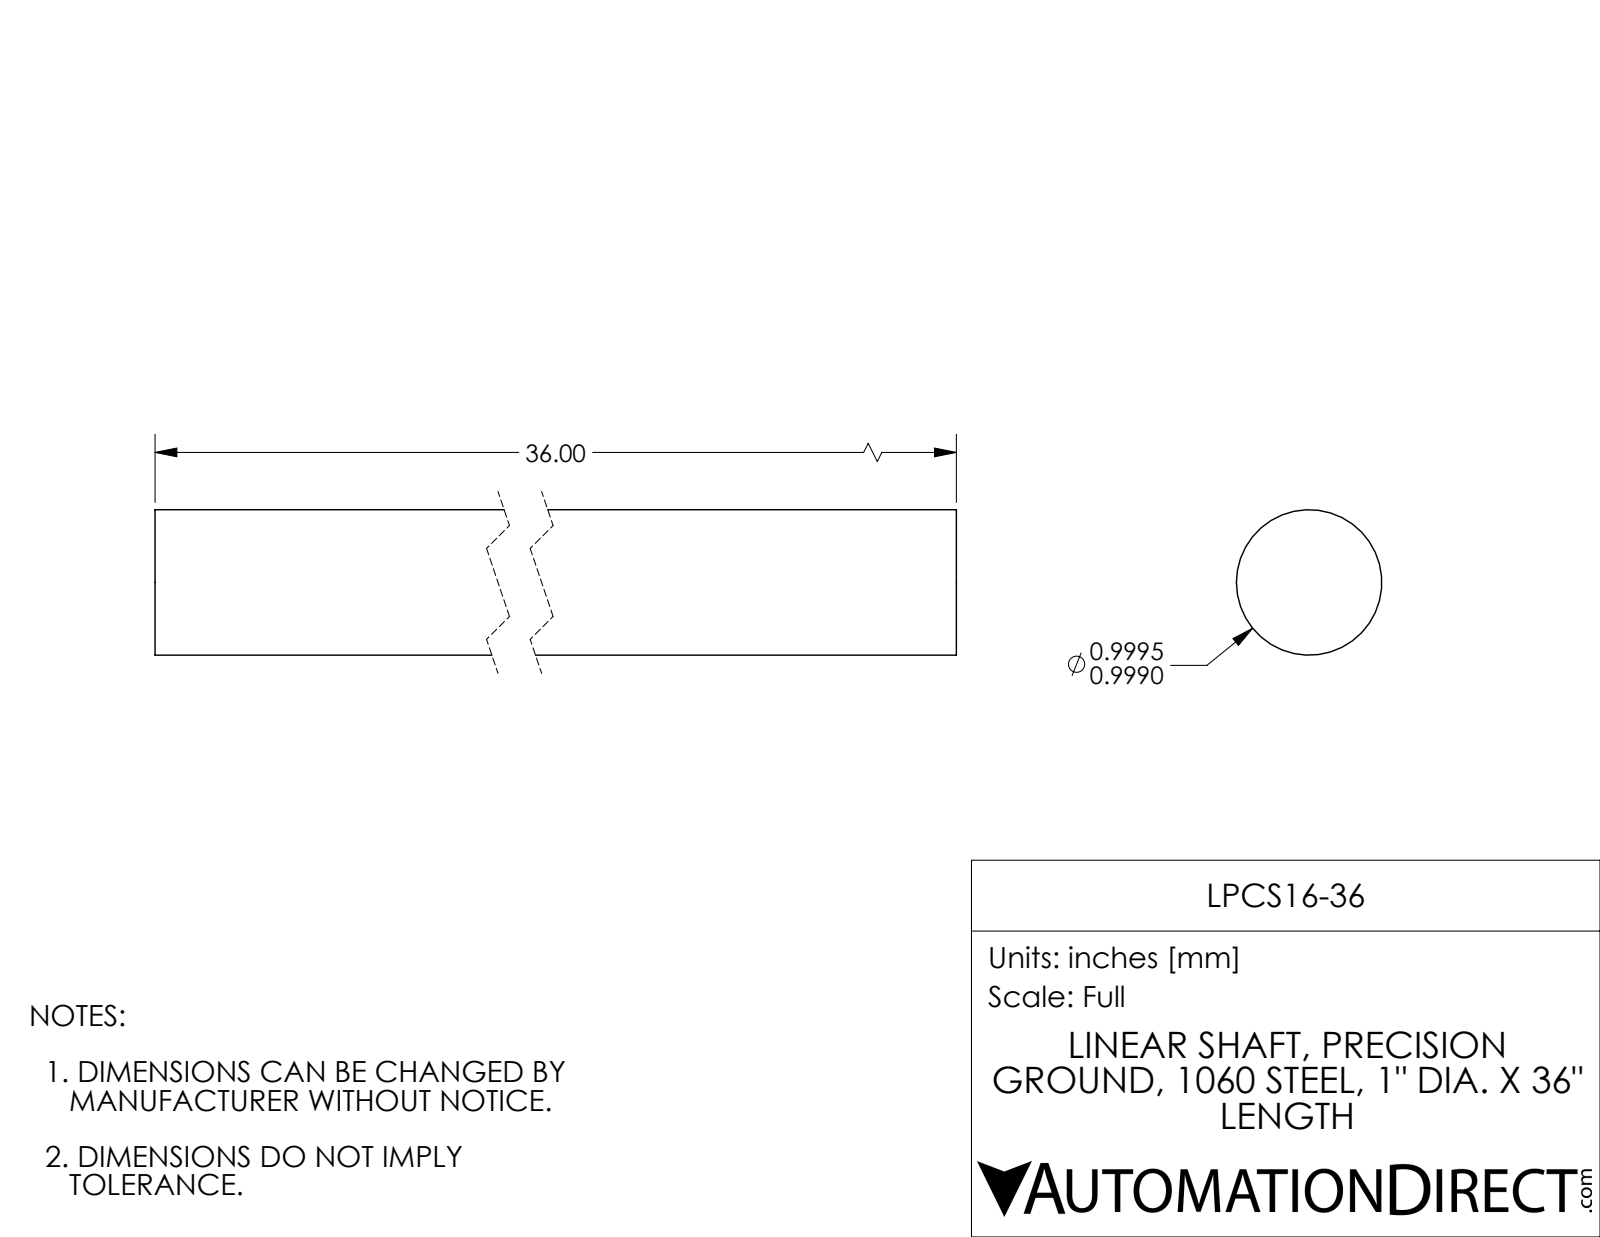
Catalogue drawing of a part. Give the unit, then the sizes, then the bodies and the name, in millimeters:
Units: millimetres
Overall size (bounding box): 914.4 × 25.4 × 25.4
Round bosses / shafts (diameter × count): ⌀25.4 ×1
Main face-to-face distances: 914.4
Volume: 462 900 mm³ · Surface area: 73 940 mm²
Bodies: 1 solid, 4 faces (2 planar, 2 cylindrical, 0 other)
Part name (STEP PRODUCT): LPCS16-36
STEP written by: SolidWorks 2017 (AUTOMOTIVE_DESIGN)
